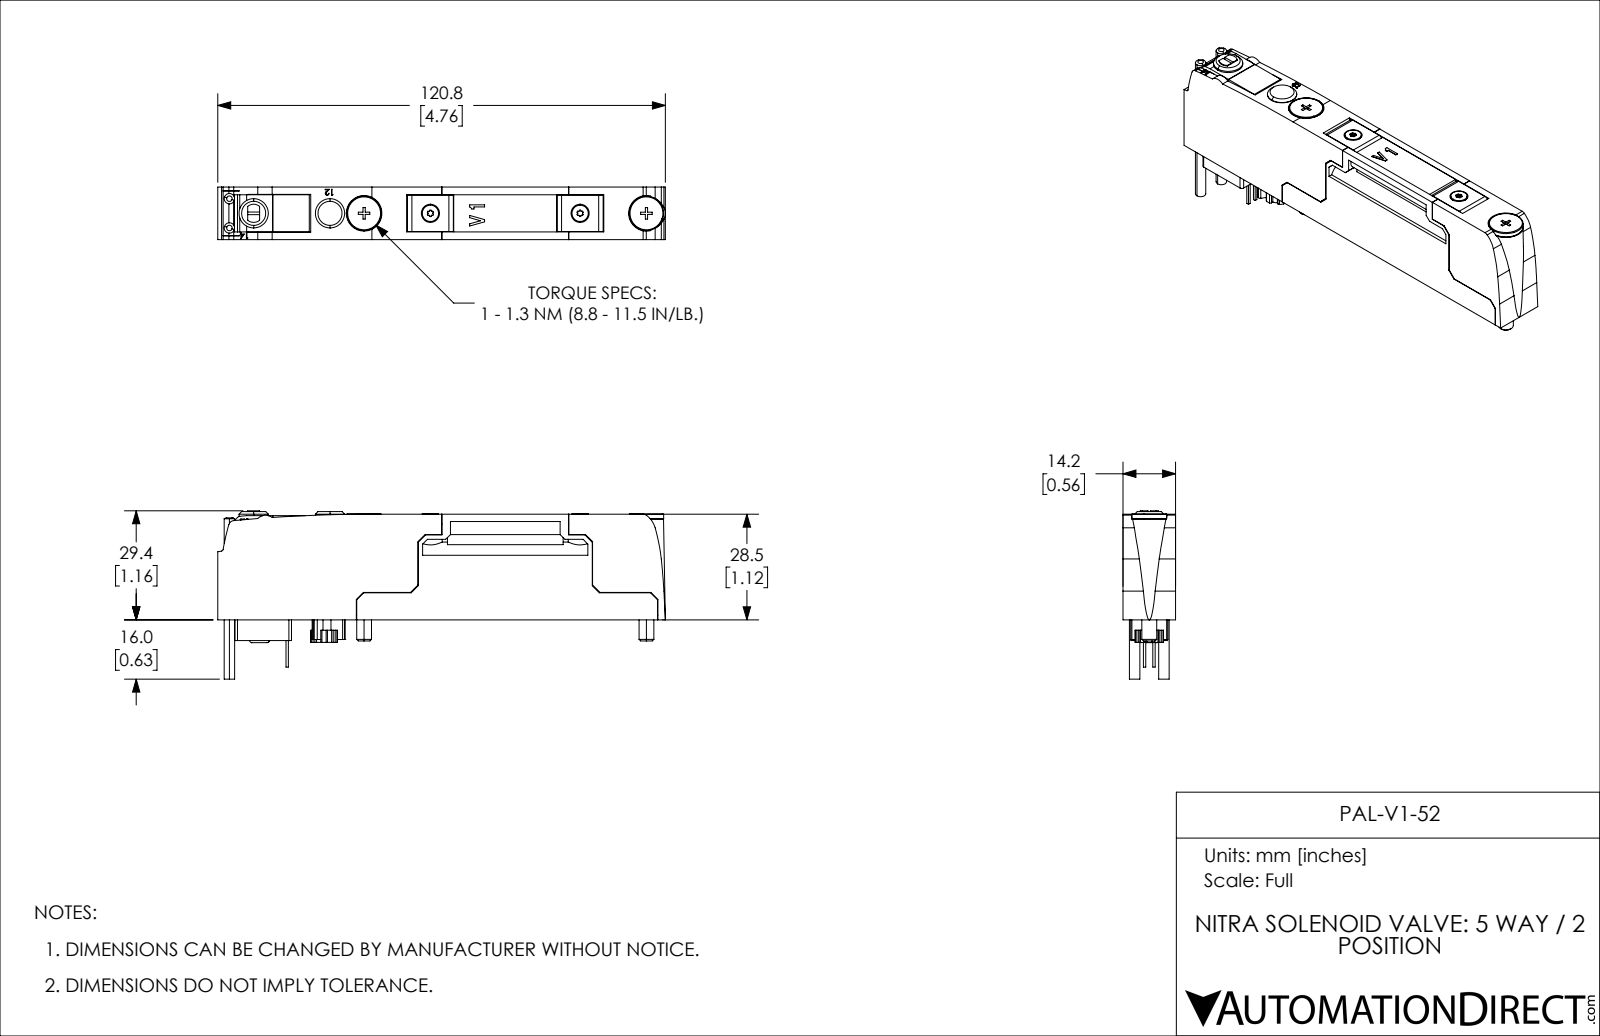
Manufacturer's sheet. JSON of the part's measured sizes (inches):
{"part_name": "PAL-V1-52", "step_written_by": "SolidWorks 2019 (CONFIG_CONTROL_DESIGN)", "units": "inches", "bodies": {"solids": 1, "faces": 578, "planar": 398, "cylindrical": 147, "other": 33}, "overall_size": [4.756, 1.787, 0.559], "volume_in3": 2.609, "surface_area_in2": 29.08, "round_holes": [[0.165, 2], [0.122, 1], [0.378, 1]], "round_bosses_or_shafts": [[0.366, 2], [0.311, 2], [0.173, 2], [0.157, 2], [0.11, 2]], "partial_cylinders_radius": [[0.016, 12], [0.024, 6], [0.028, 4], [0.047, 4], [0.059, 3], [0.026, 2], [0.028, 2], [0.035, 2]], "face_to_face_distances": [0.559, 0.083, 0.476, 0.394, 0.087, 1.122, 0.252, 0.677, 0.835, 0.409], "hole_center_spacings": [1.11, 3, 4.11]}
